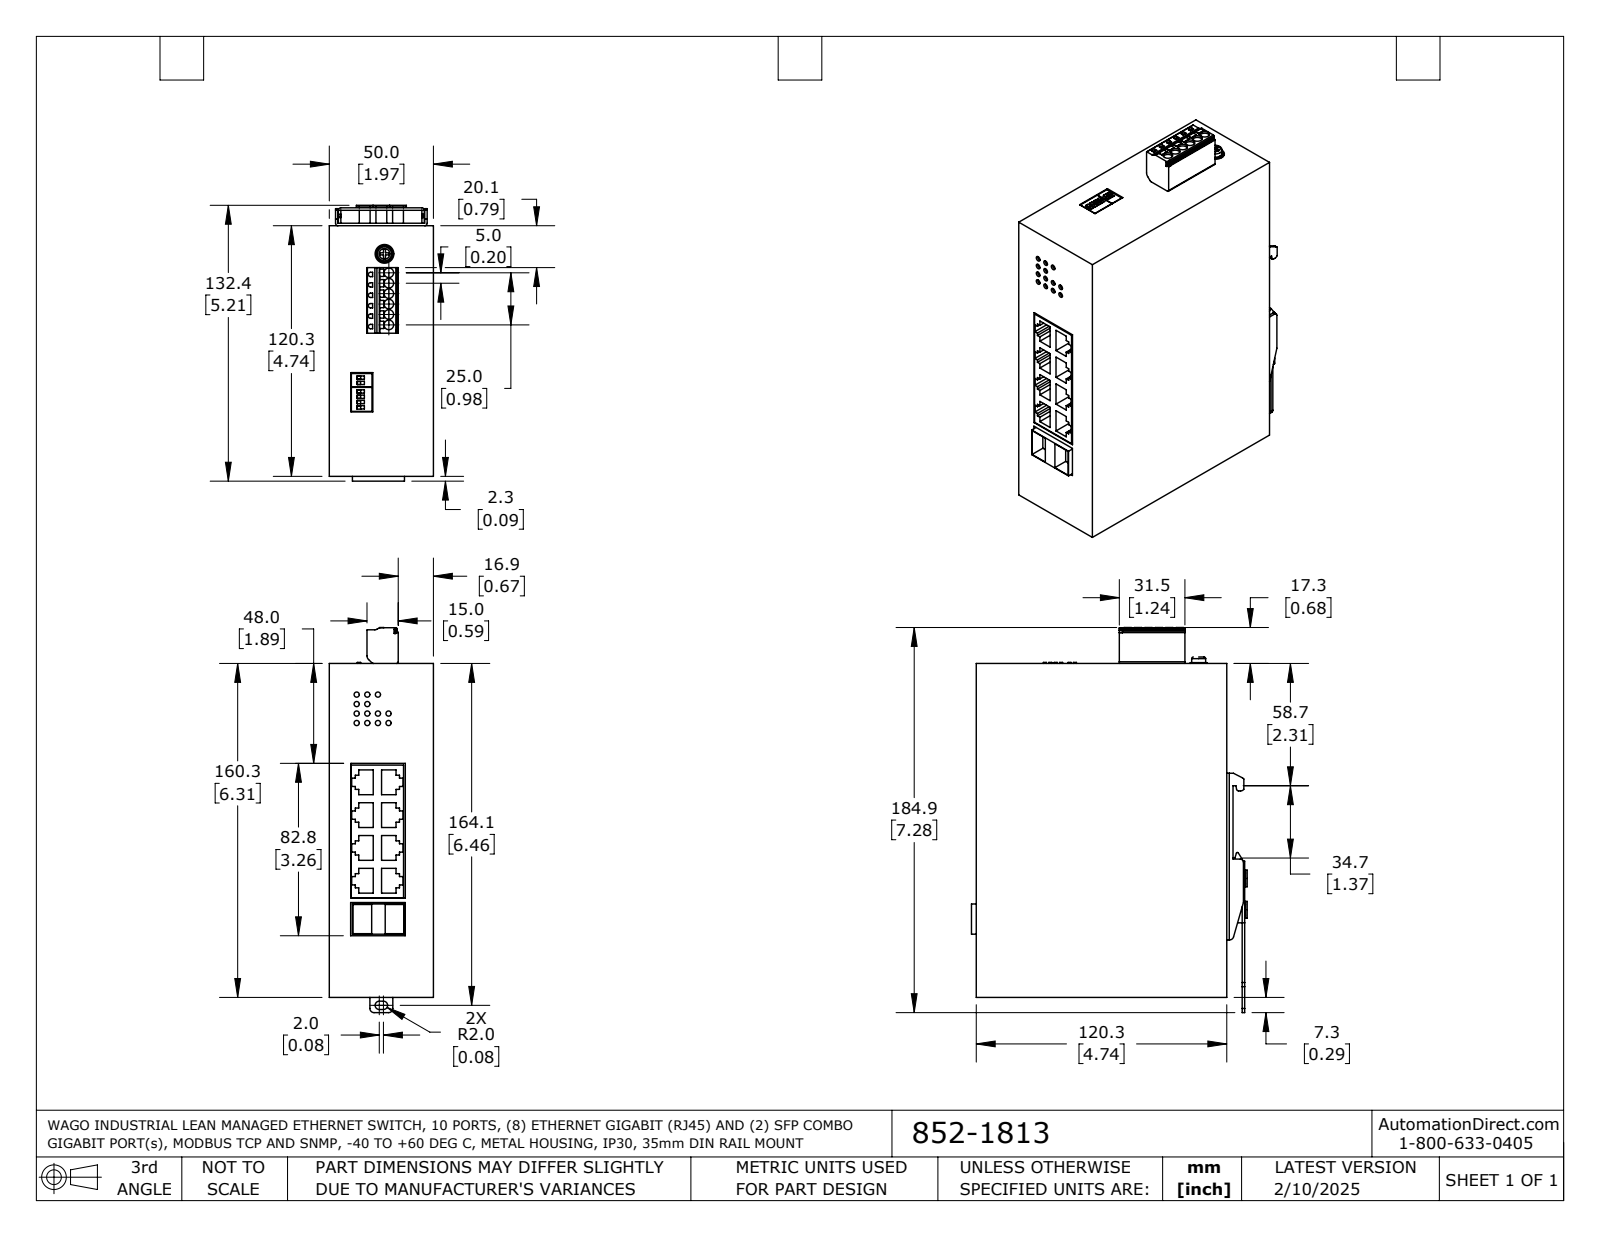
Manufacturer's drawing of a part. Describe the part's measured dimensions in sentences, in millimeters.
The part is named "852-1813". Its 3-D file was written by "SolidWorks 2021 (AUTOMOTIVE_DESIGN)". It is 1 solid with 573 faces: 407 planar, 151 cylindrical and 15 other. Overall it measures 184.9 by 132.4 by 50 millimeters. Its volume is 969 000 cubic millimeters and its surface area 85 160 square millimeters. Round holes: 13 of diameter 2.5, 6 of diameter 4.6, 2 of diameter 10, 1 of diameter 9. Round bosses or shafts: 4 of diameter 8, 3 of diameter 5.2, 1 of diameter 6.7. Partial cylindrical surfaces (rounded edges, fillets, slot ends): 14 of radius 0.1, 10 of radius 2, 6 of radius 1, 6 of radius 2.6, 5 of radius 1.2, 4 of radius 0.5, 3 of radius 0.2, 1 of radius 0.8. The main face-to-face distances are 50, 1.2, 160.3, 120.3, 7.4, 121.5, 6.2, 8.6, 127.7, 128.9. The hole center spacings are 6.8, 5.1, 4.5, 10.4, 11.2, 5, 9.1, 10.2.
